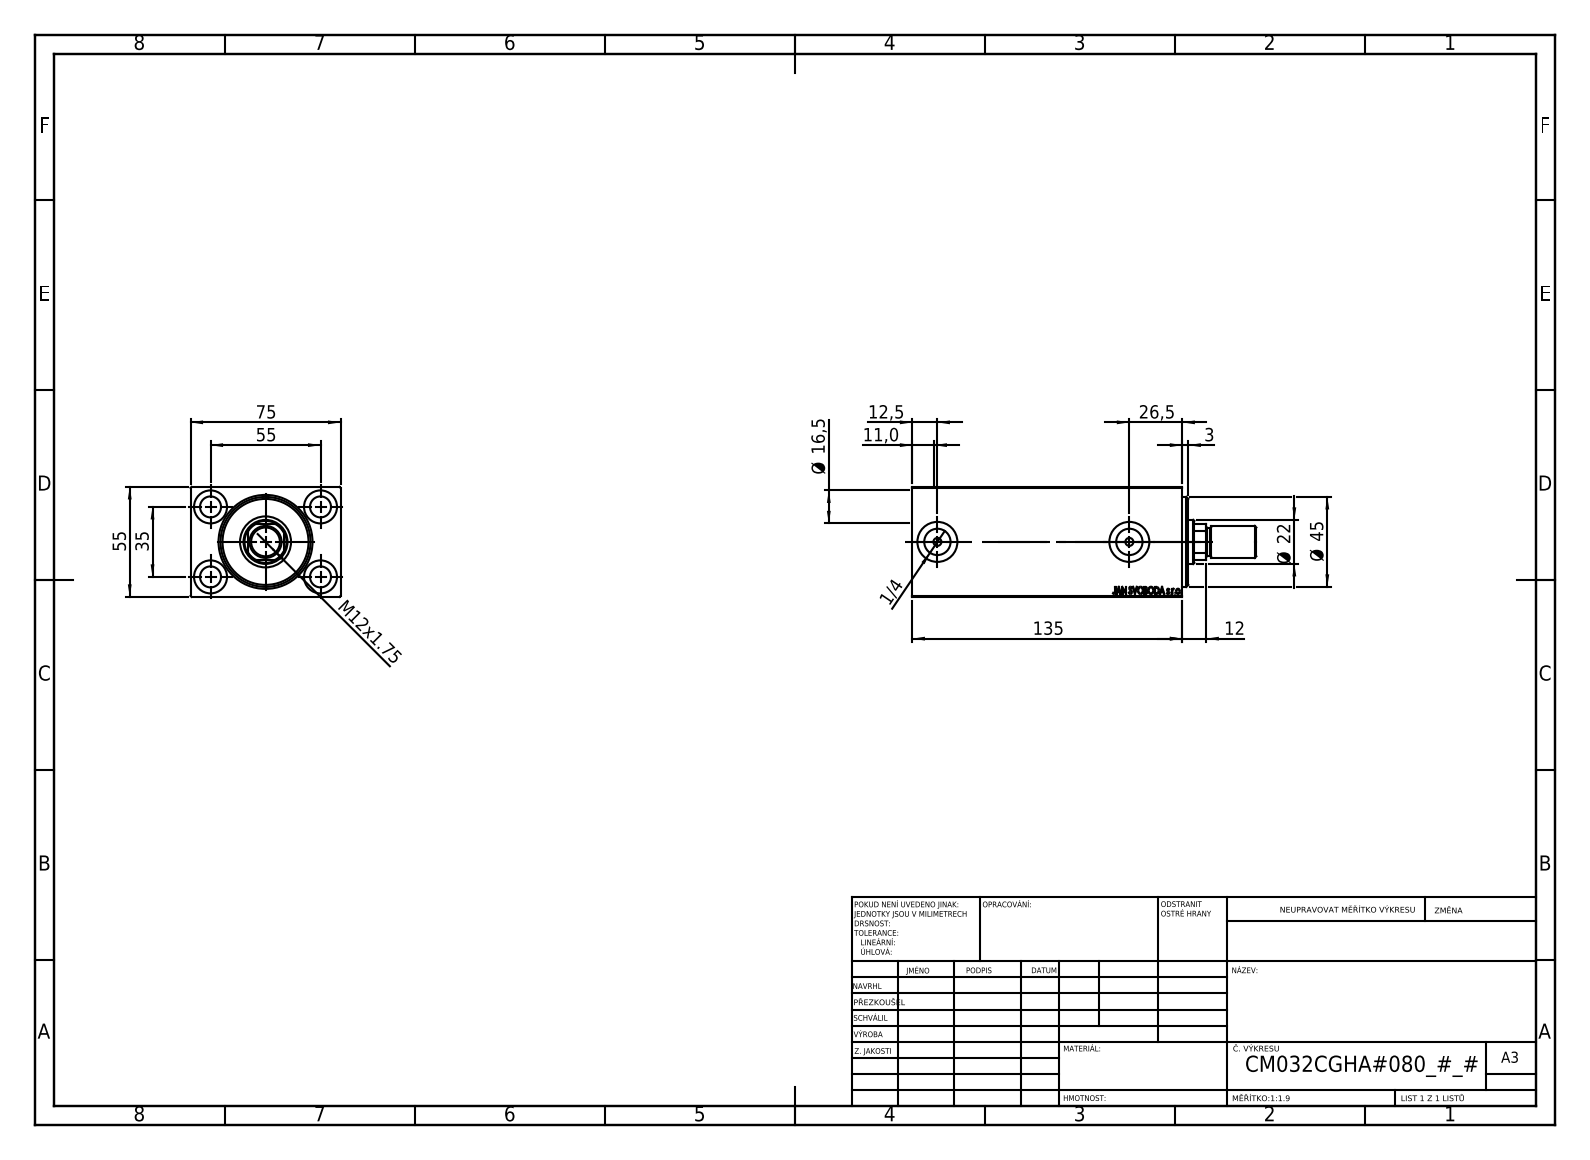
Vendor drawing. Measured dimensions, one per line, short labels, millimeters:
name: V450CM_C_VCP; V450CM_MALE_METRIC; V450CM_C_Body; V450CM_VC_B
written by: SolidWorks 2019 (CONFIG_CONTROL_DESIGN)
unit: mm
bodies: 4 solids, 875 faces (411 planar, 64 cylindrical, 400 other)
size: 172 × 75 × 55
volume: 471 830 mm³; area: 95 636 mm²
holes: 5× ⌀10.5, 4× ⌀16.5, 2× ⌀4, 2× ⌀13.16, 2× ⌀20, 1× ⌀22, 1× ⌀25.5, 1× ⌀32, 1× ⌀34, 1× ⌀45
bosses: 1× ⌀16, 1× ⌀14
rounds: 1× R10.5
face distances: 55, 75, 10, 125, 135, 130, 5, 120, 113, 11
hole spacings: 32.6, 35, 55, 65.19, 96
